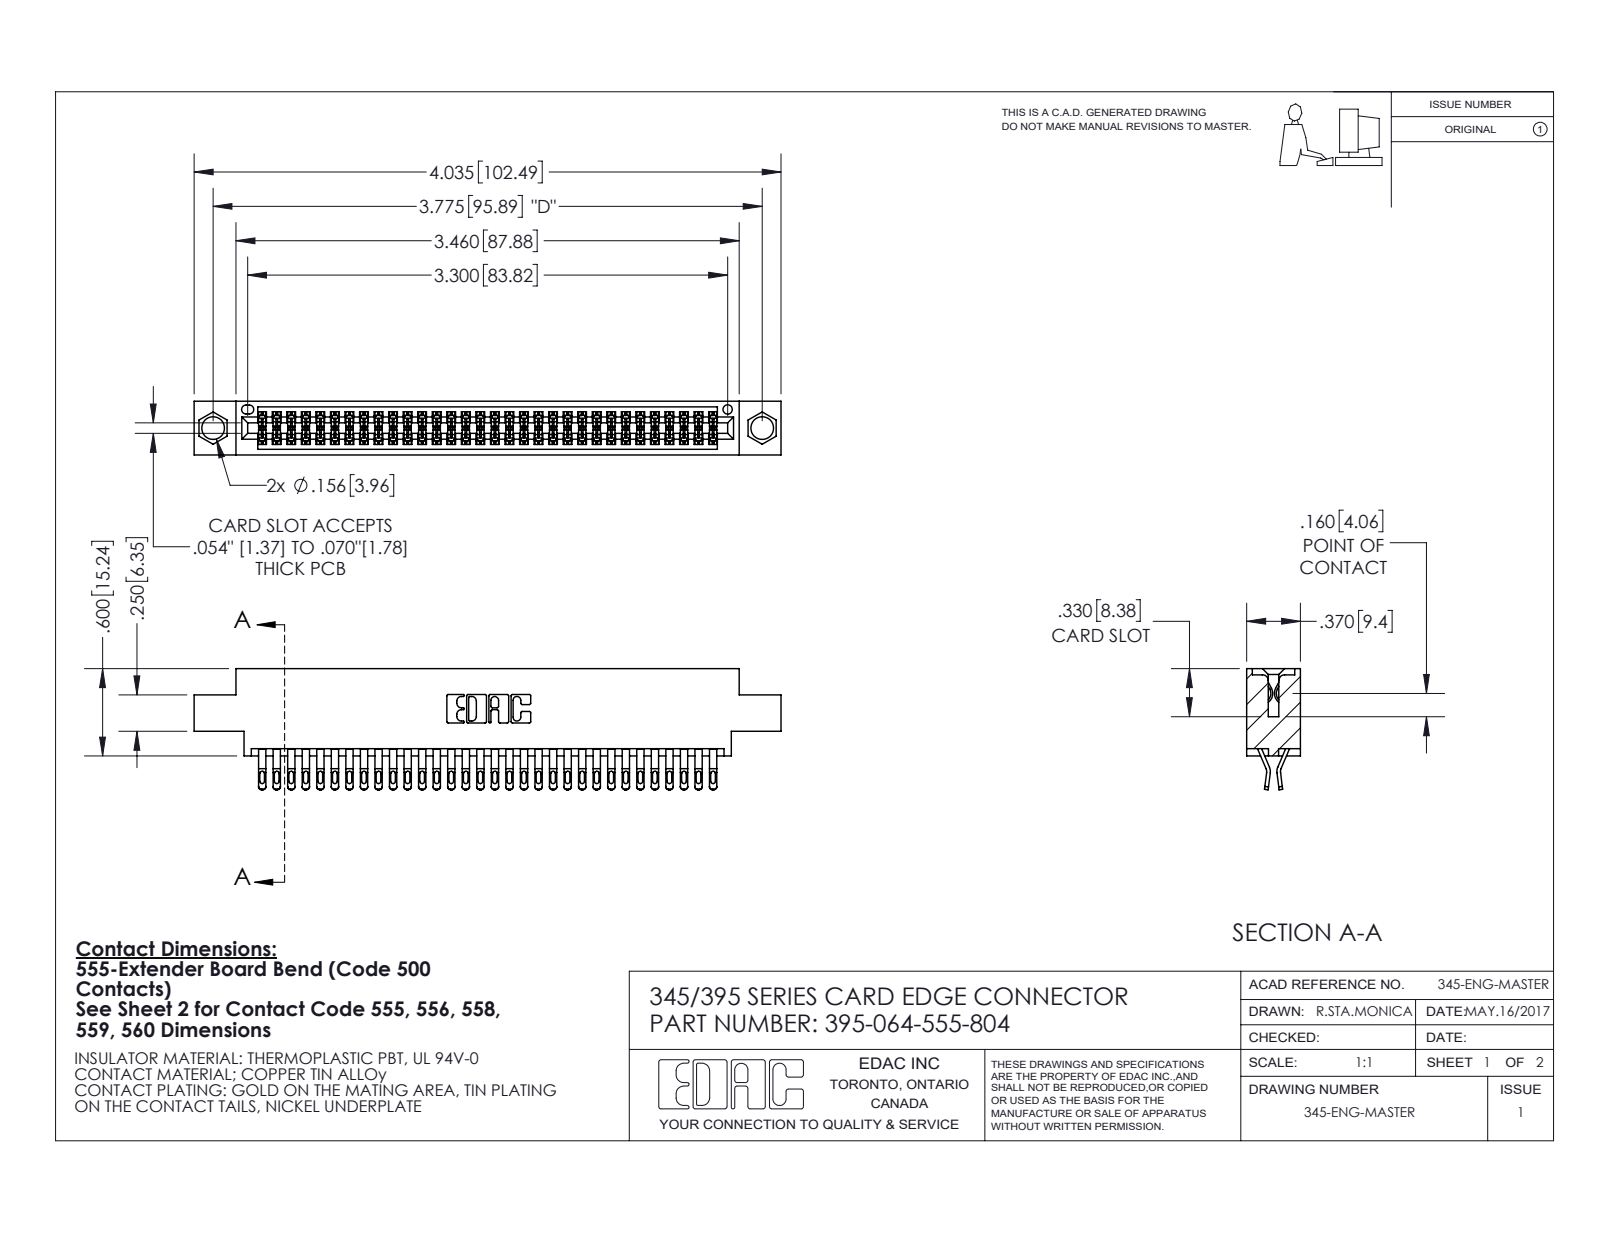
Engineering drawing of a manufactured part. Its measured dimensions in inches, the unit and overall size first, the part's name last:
Units: inches
Overall size (bounding box): 4.035 × 0.832 × 0.37
Round holes (diameter × count): ⌀0.156 ×2, ⌀0.064 ×1
Partial cylindrical surfaces — rounded edges, fillets, slot ends (radius × count): R0.016 ×160, R0.02 ×128, R0.006 ×96, R0.01 ×22, R0.007 ×6, R0.031 ×6, R0.026 ×3, R0.01 ×2
Main face-to-face distances: 0.298, 0.072, 0.37, 0.025, 0.2, 0.098, 0.272, 0.225, 0.175, 0.149
Hole centre spacings: 0.27, 3.54, 3.775
Volume: 0.6 in³ · Surface area: 23.21 in²
Bodies: 65 solids, 3728 faces (2082 planar, 1646 cylindrical, 0 other)
Part name (STEP PRODUCT): 345 Part_0.170 Offset - 0.156 Dia-TI; 395-064-555-804; 345-292-001_555 Tail
STEP written by: SolidWorks 2020 (CONFIG_CONTROL_DESIGN)
